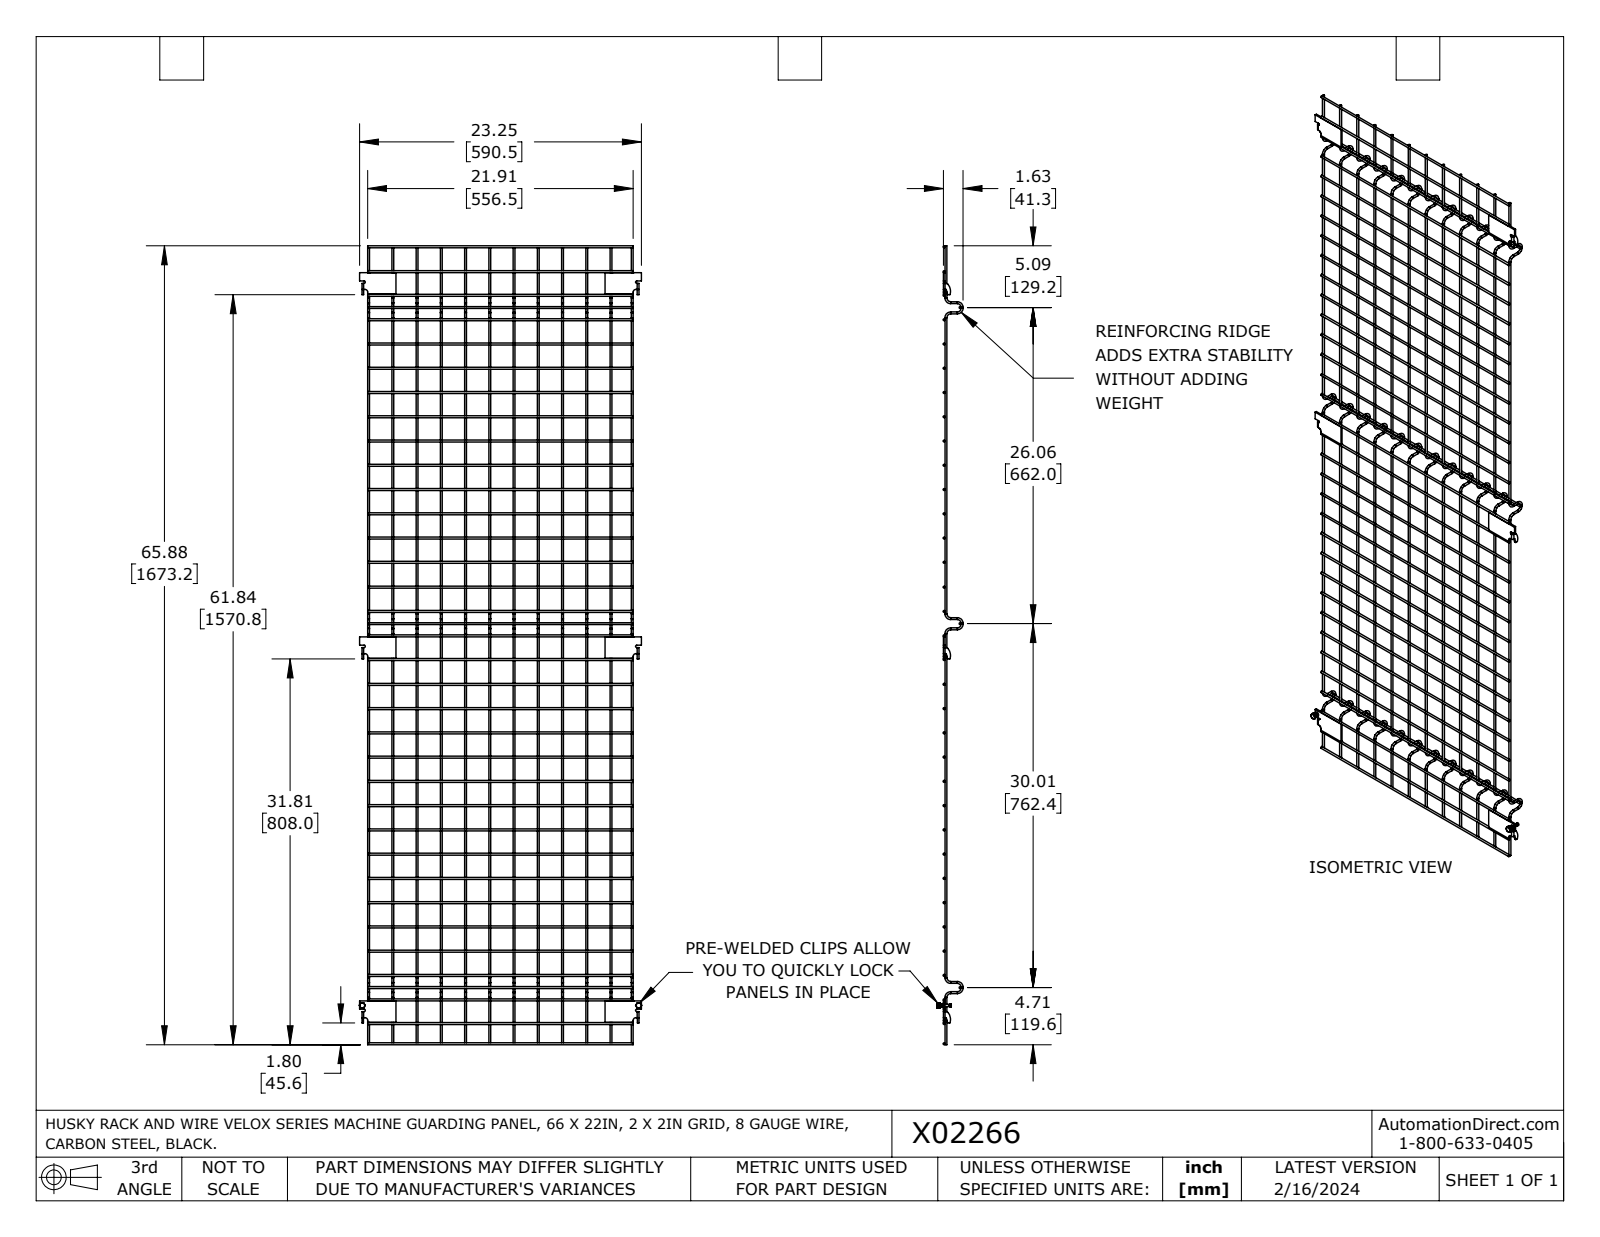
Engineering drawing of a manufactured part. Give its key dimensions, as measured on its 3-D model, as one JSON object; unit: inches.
{"part_name": "X02266", "step_written_by": "SolidWorks 2023 (AUTOMOTIVE_DESIGN)", "units": "inches", "bodies": {"solids": 59, "faces": 615, "planar": 206, "cylindrical": 241, "other": 168}, "overall_size": [65.875, 23.313, 2.103], "volume_in3": 37.78, "surface_area_in2": 916.5, "round_holes": [[0.201, 2], [0.25, 2]], "round_bosses_or_shafts": [[0.16, 133], [0.39, 2], [0.245, 2], [0.187, 2]], "partial_cylinders_radius": [[0.1, 6], [0.218, 6], [0.25, 3], [0.865, 3], [0.009, 2], [0.067, 2], [0.134, 2]], "face_to_face_distances": [0.134, 0.125, 1.765, 0.467, 22.377, 30.031, 60.047, 30.016, 2.798, 20.046], "hole_center_spacings": [22.808]}
